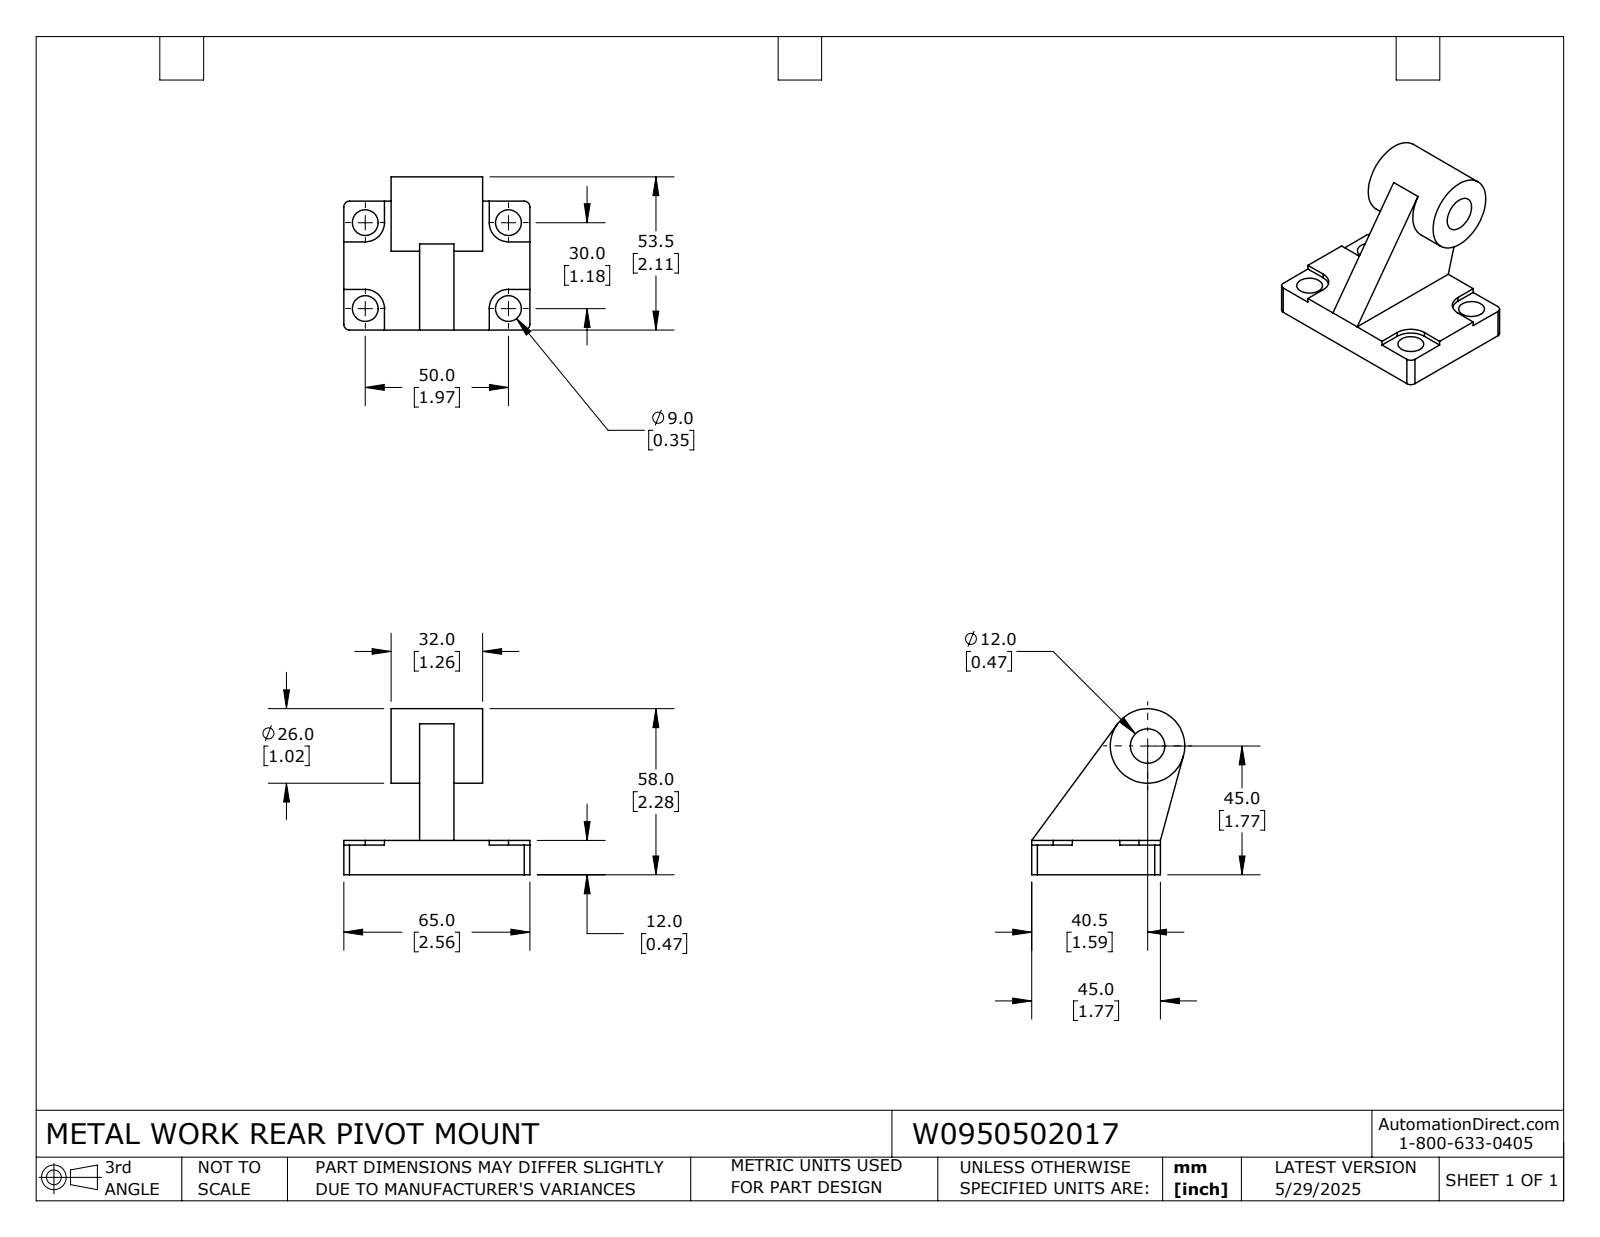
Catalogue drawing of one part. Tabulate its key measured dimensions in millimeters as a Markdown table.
| quantity | value |
| --- | --- |
| part name | W0950502017 |
| STEP written by | SolidWorks 2024 (CONFIG_CONTROL_DESIGN) |
| units | millimeters |
| bodies | 1 solid, 50 faces (30 planar, 20 cylindrical, 0 other) |
| overall size | 65 × 58 × 53.5 |
| volume | 54 924 mm³ |
| surface area | 15 839 mm² |
| round holes (diameter × count) | 9 × 4, 12 × 1 |
| round bosses / shafts (diameter × count) | 26 × 1 |
| partial cylindrical surfaces (radius × count) | 2 × 4, 6.7 × 4 |
| main face-to-face distances | 12, 26.5, 22, 16.5, 38.5, 48.5, 10, 45, 10.4, 1.6 |
| hole center spacings | 30, 50, 58.31 |
